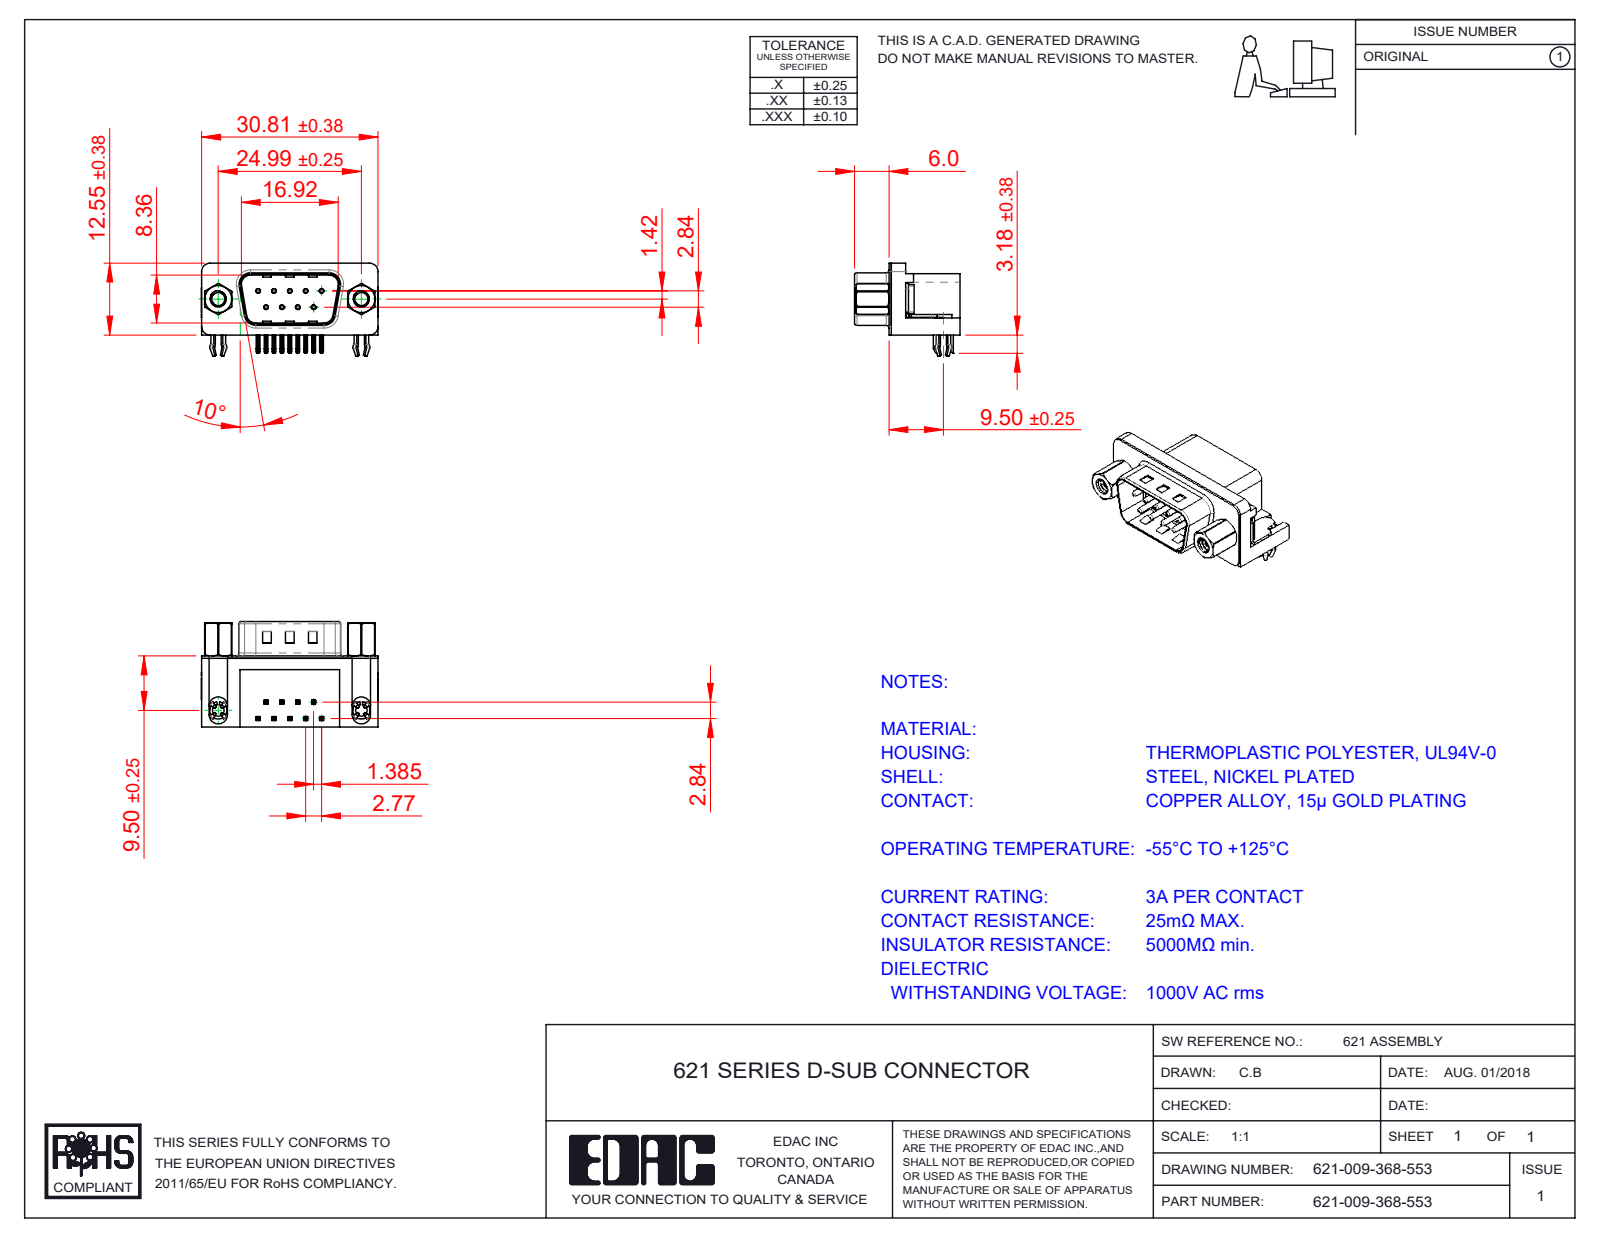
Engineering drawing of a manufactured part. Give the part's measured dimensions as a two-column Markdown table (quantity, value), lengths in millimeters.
| quantity | value |
| --- | --- |
| part name | 621-009-368-553; 621 4-40 Threaded Rivet; 621 Shell_9 Socket; 621 Housing_9 Socket (+4 more) |
| STEP written by | SolidWorks 2016 (CONFIG_CONTROL_DESIGN) |
| units | millimeters |
| bodies | 17 solids, 1147 faces (595 planar, 399 cylindrical, 153 other) |
| overall size | 30.89 × 18.4 × 15.73 |
| volume | 3 471 mm³ |
| surface area | 4 983 mm² |
| round holes (diameter × count) | 0.35 × 9, 0.8 × 9, 2.26 × 4, 2.29 × 2, 4 × 2, 4.8 × 2, 5 × 2 |
| round bosses / shafts (diameter × count) | 0.75 × 9, 4.9 × 2, 4.75 × 2, 3.9 × 2, 3.26 × 2, 2.79 × 2 |
| partial cylindrical surfaces (radius × count) | 0.25 × 44, 0.12 × 18, 1 × 16, 0.5 × 9, 1.5 × 8, 1.6 × 8, 0.9 × 4, 2 × 4 |
| main face-to-face distances | 0.4, 12, 12.4, 10.35, 9.5, 2.5, 2.9, 0.5, 2.1, 0.35 |
| hole center spacings | 3.16, 2.77, 5.54, 5.03, 5.04, 8.31, 7.48, 7.49 |
